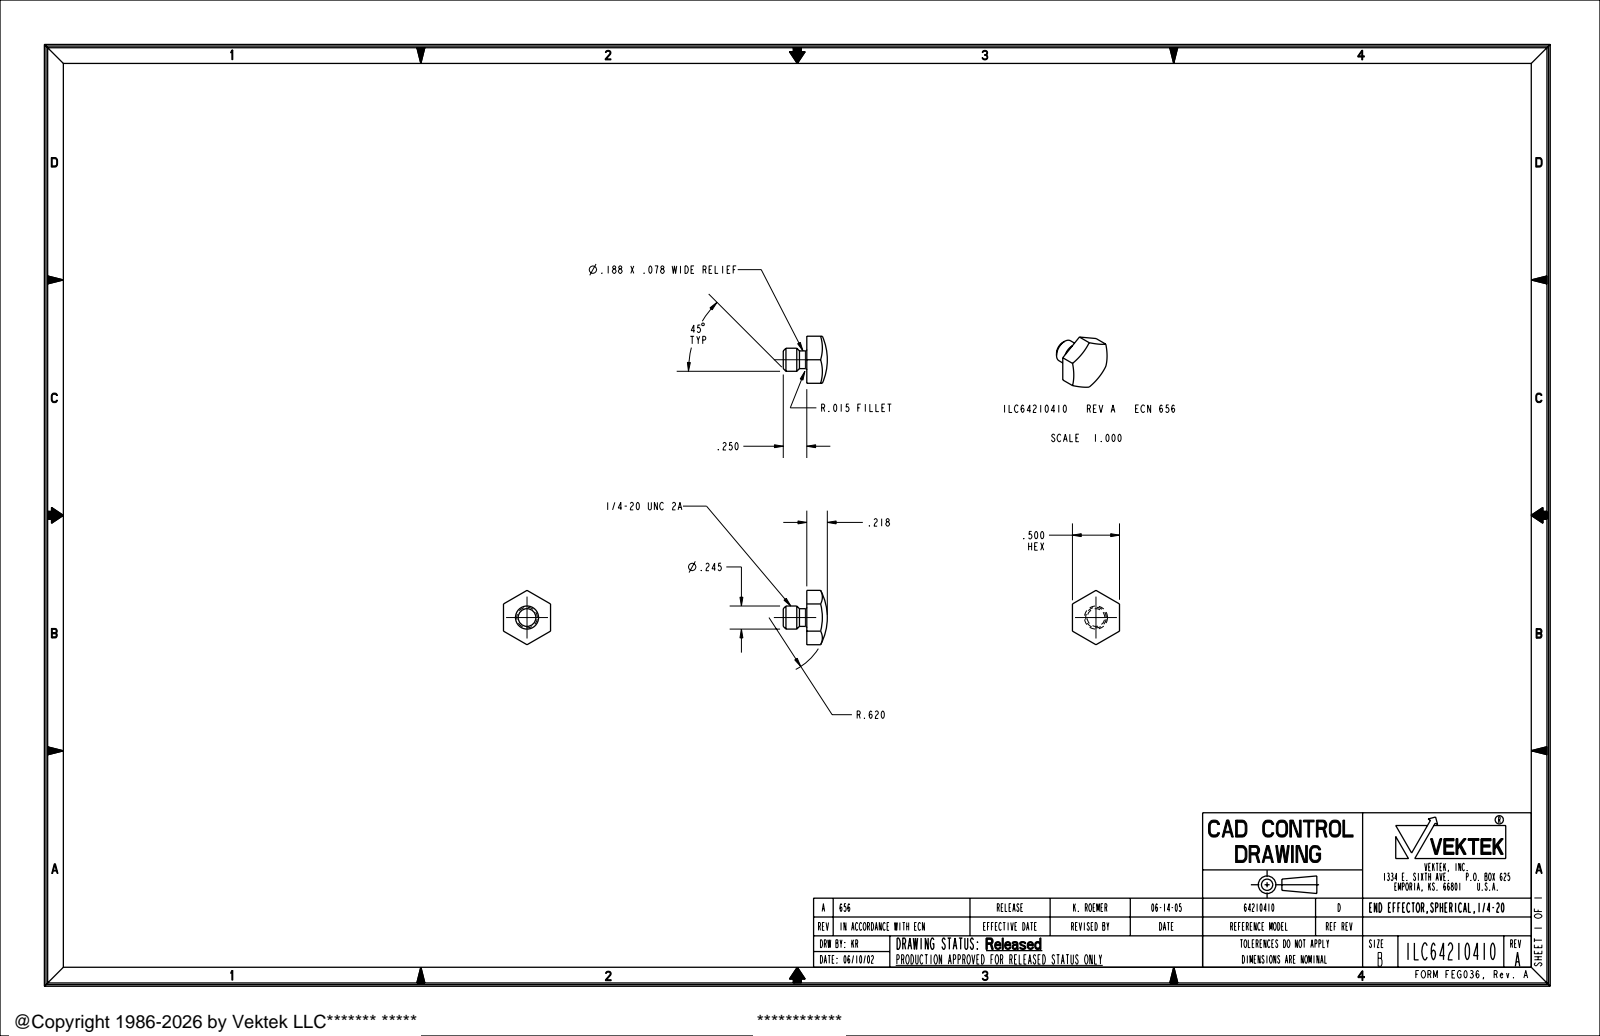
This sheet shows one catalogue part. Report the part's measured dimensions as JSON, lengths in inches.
{"part_name": "ILC64210410", "step_written_by": "PRO/ENGINEER BY PARAMETRIC TECHNOLOGY CORPORATION, 2004290 (AUTOMOTIVE_DESIGN_CC2)", "units": "inches", "bodies": {"solids": 1, "faces": 20, "planar": 8, "cylindrical": 4, "other": 8}, "overall_size": [0.577, 0.5, 0.468], "volume_in3": 0.051, "surface_area_in2": 0.905, "round_bosses_or_shafts": [[0.245, 1], [0.188, 1]], "face_to_face_distances": [0.5, 0.25]}
